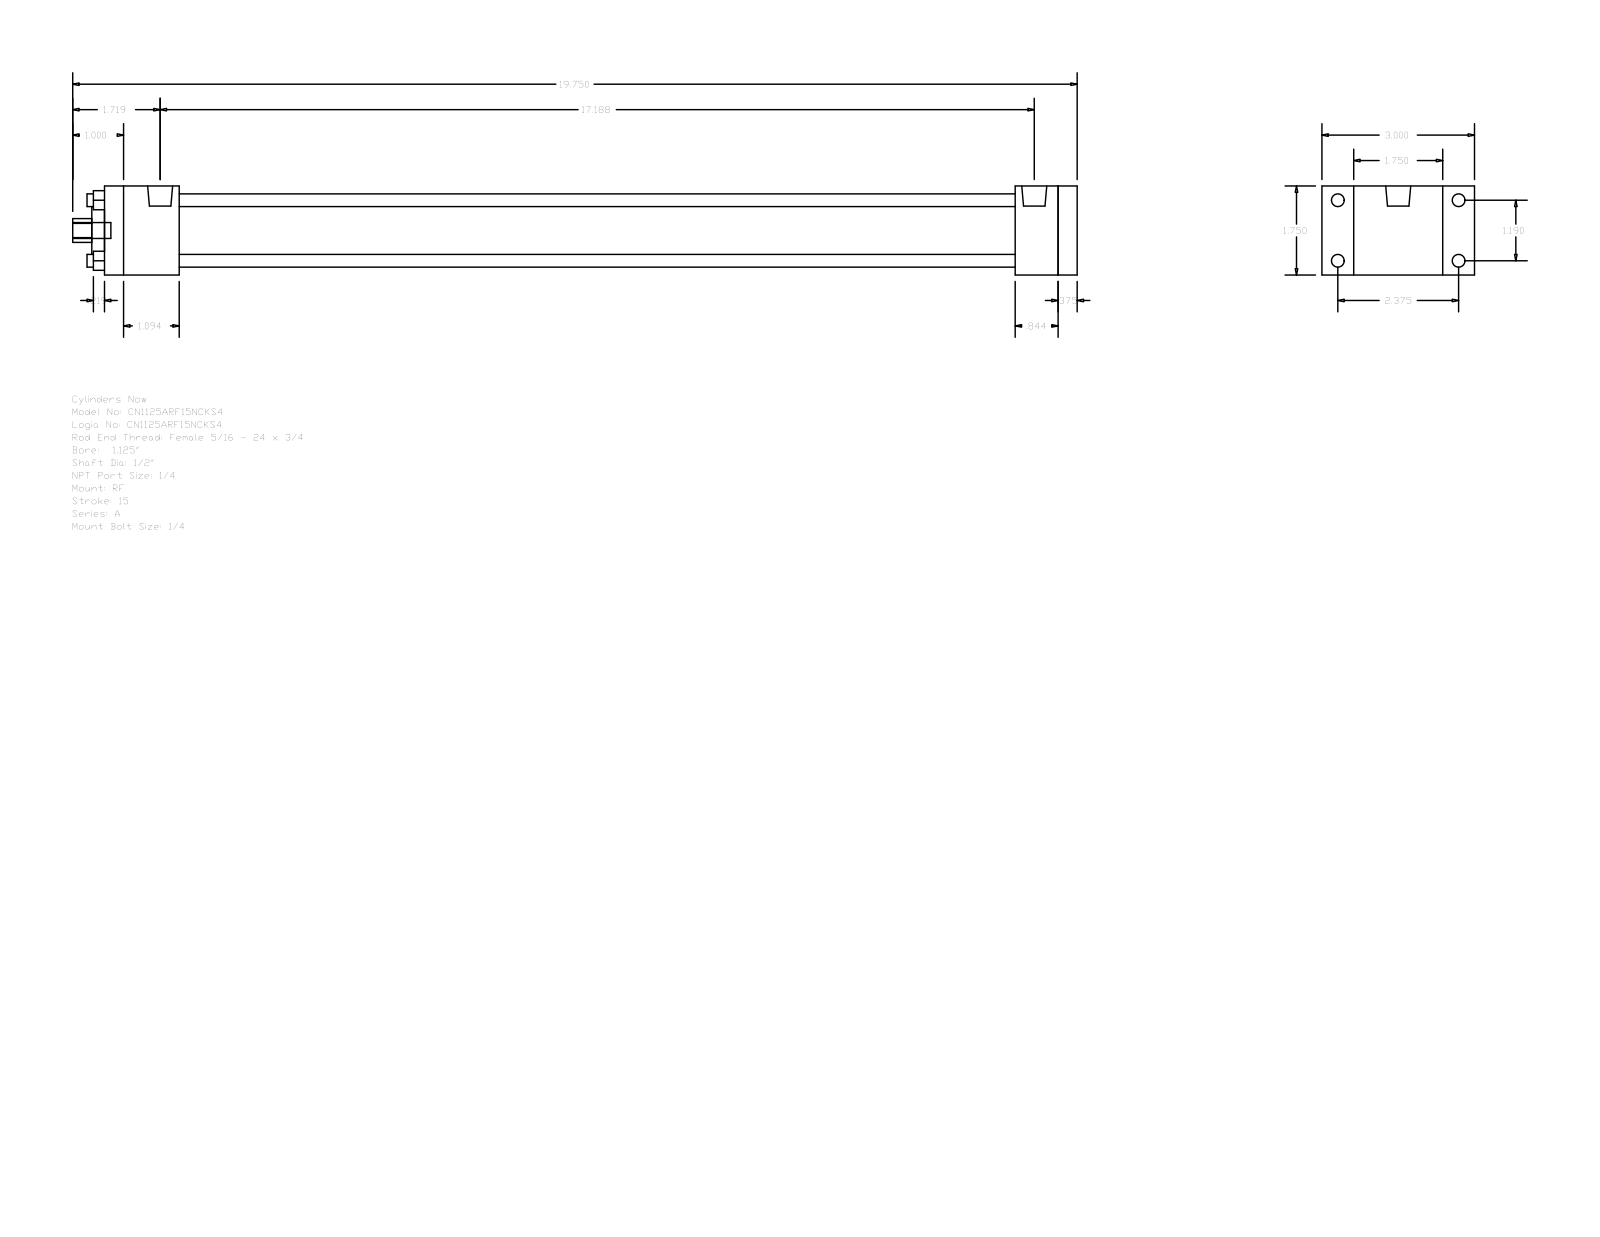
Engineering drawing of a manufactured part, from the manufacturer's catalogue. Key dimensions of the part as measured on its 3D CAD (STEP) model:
Part name (STEP PRODUCT): A_RF__0112_0.5
STEP written by: GSSL Pune (CONFIG_CONTROL_DESIGN)
Units: millimetres
Bodies: 0 solids, 92 faces (64 planar, 28 cylindrical, 0 other)
Overall size (bounding box): 501.65 × 76.2 × 44.45
Round holes (diameter × count): ⌀6.35 ×4, ⌀12.7 ×1, ⌀23.81 ×1, ⌀31.88 ×1
Round bosses / shafts (diameter × count): ⌀6.35 ×4, ⌀5.56 ×4, ⌀12.49 ×2, ⌀7.94 ×1
Partial cylindrical surfaces — rounded edges, fillets, slot ends (radius × count): R5.94 ×1
Main face-to-face distances: 44.46, 9.53, 485.77, 476.24, 37.3, 454.81, 417.51, 438.94, 448.47, 21.43
Hole centre spacings: 21.37, 30.22, 42.74
